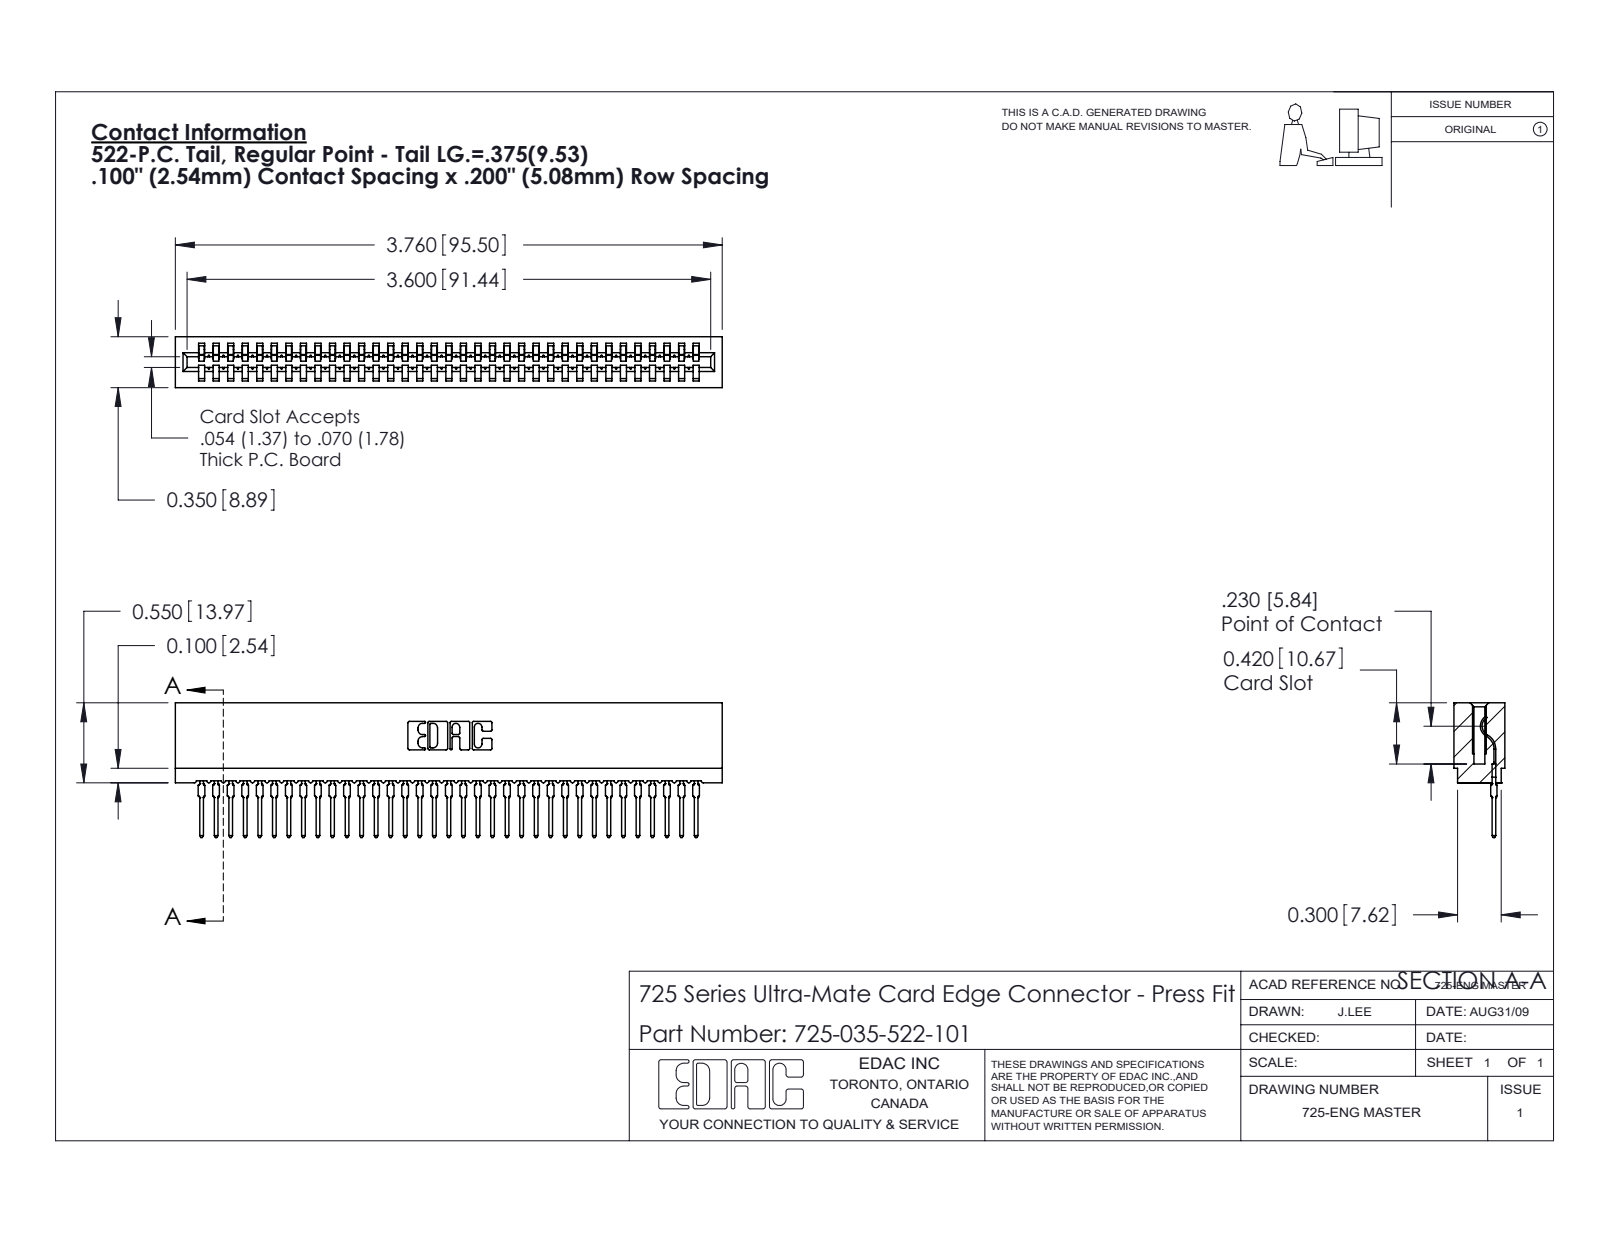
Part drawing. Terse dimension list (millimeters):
name: 725 Part_Insulator Option - 01; 725-035-522-101; 745-292-001_522
written by: SolidWorks 2020 (CONFIG_CONTROL_DESIGN)
unit: mm
bodies: 36 solids, 4015 faces (2400 planar, 705 cylindrical, 910 other)
size: 95.5 × 23.5 × 8.9
volume: 7 310 mm³; area: 14 020 mm²
rounds: 70× R0.4, 70× R0.5, 22× R0.3, 6× R0.2, 6× R0.8, 4× R0.1, 4× R0.3, 3× R0.7
face distances: 8.9, 5.4, 3.5, 2.5, 5.1, 1.1, 7.7, 2.4, 4.2, 1.6
